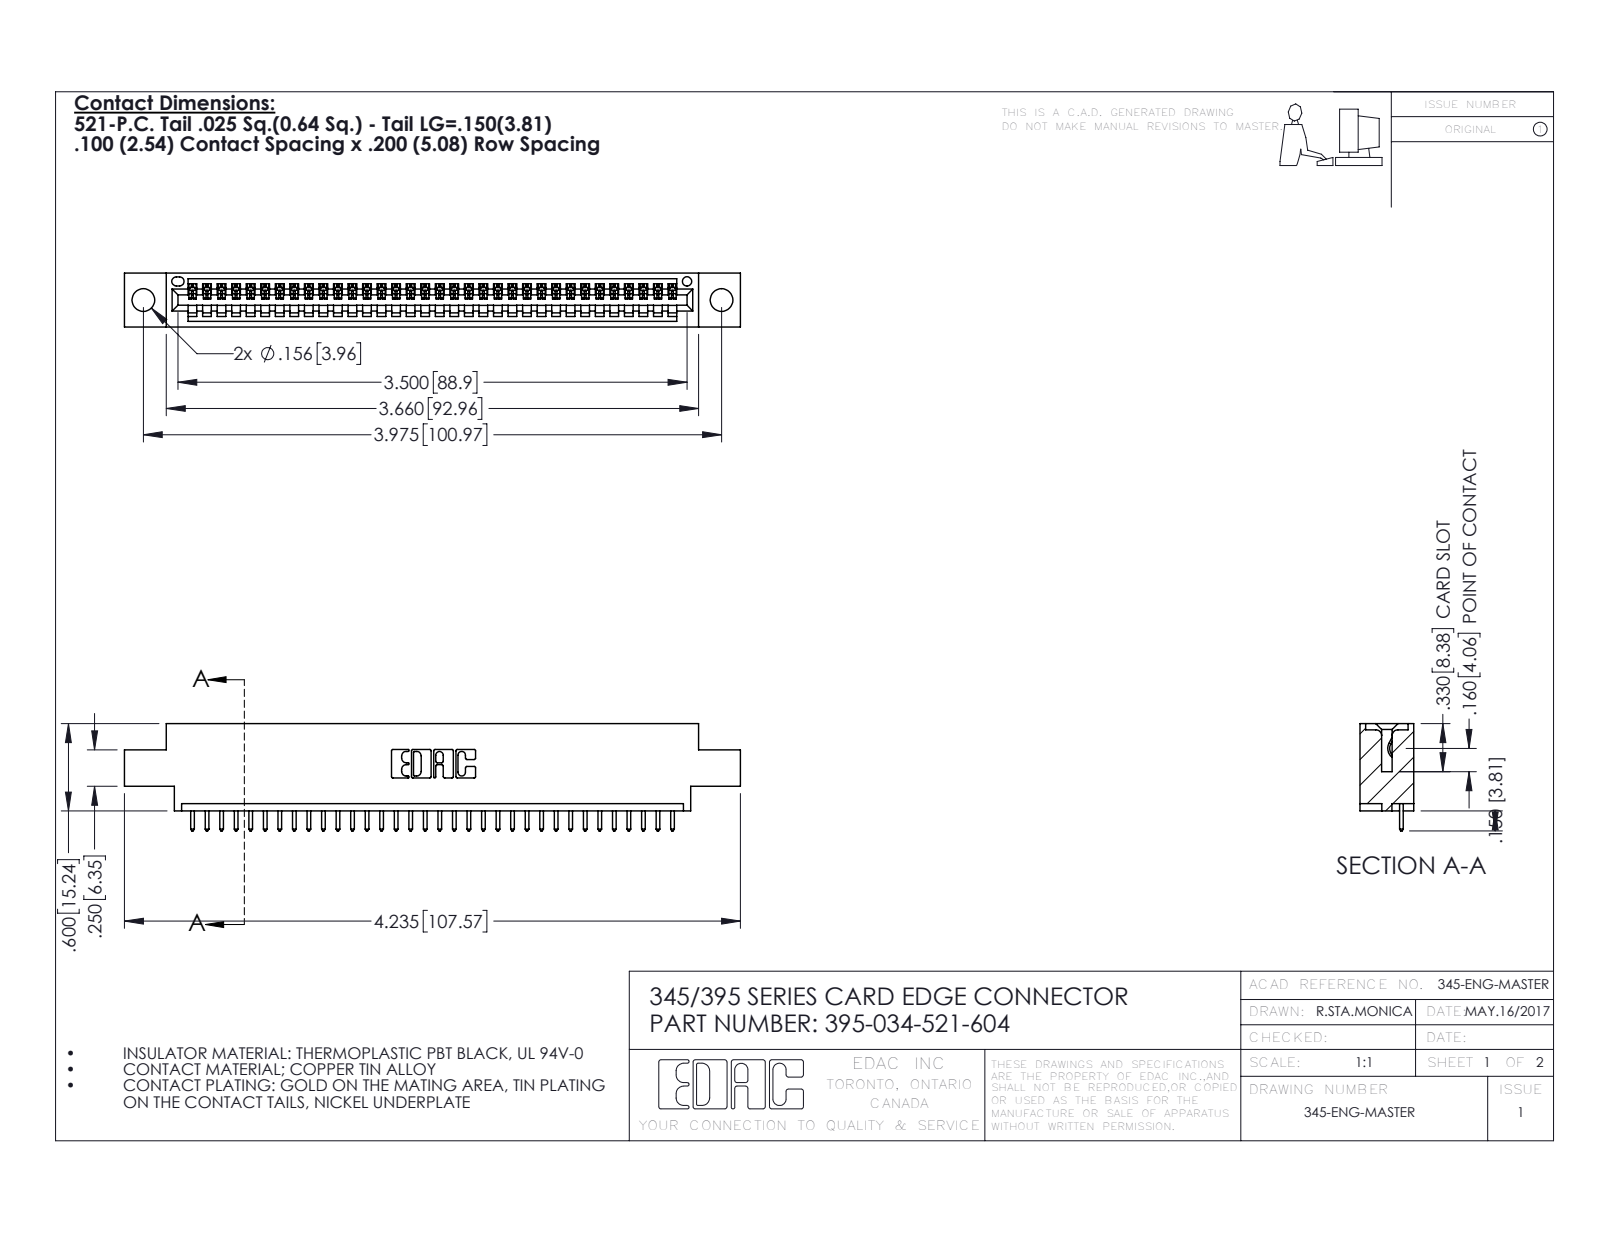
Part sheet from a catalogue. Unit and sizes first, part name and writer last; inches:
Units: inches
Overall size (bounding box): 4.235 × 0.737 × 0.37
Round holes (diameter × count): ⌀0.156 ×2, ⌀0.064 ×1
Partial cylindrical surfaces — rounded edges, fillets, slot ends (radius × count): R0.006 ×68, R0.01 ×68, R0.01 ×22, R0.007 ×6, R0.031 ×6, R0.026 ×3, R0.031 ×2, R0.04 ×2
Main face-to-face distances: 0.298, 0.072, 0.37, 0.2, 0.098, 0.272, 0.025, 0.225, 0.175, 0.149
Hole centre spacings: 0.27, 3.74, 3.975
Volume: 0.601 in³ · Surface area: 19.44 in²
Bodies: 35 solids, 2102 faces (1444 planar, 658 cylindrical, 0 other)
Part name (STEP PRODUCT): 345-292-001_345-293-121; 395-034-521-604; 345 Part_0.170 Offset - 0.156 Dia-TH
STEP written by: SolidWorks 2016 (CONFIG_CONTROL_DESIGN)
